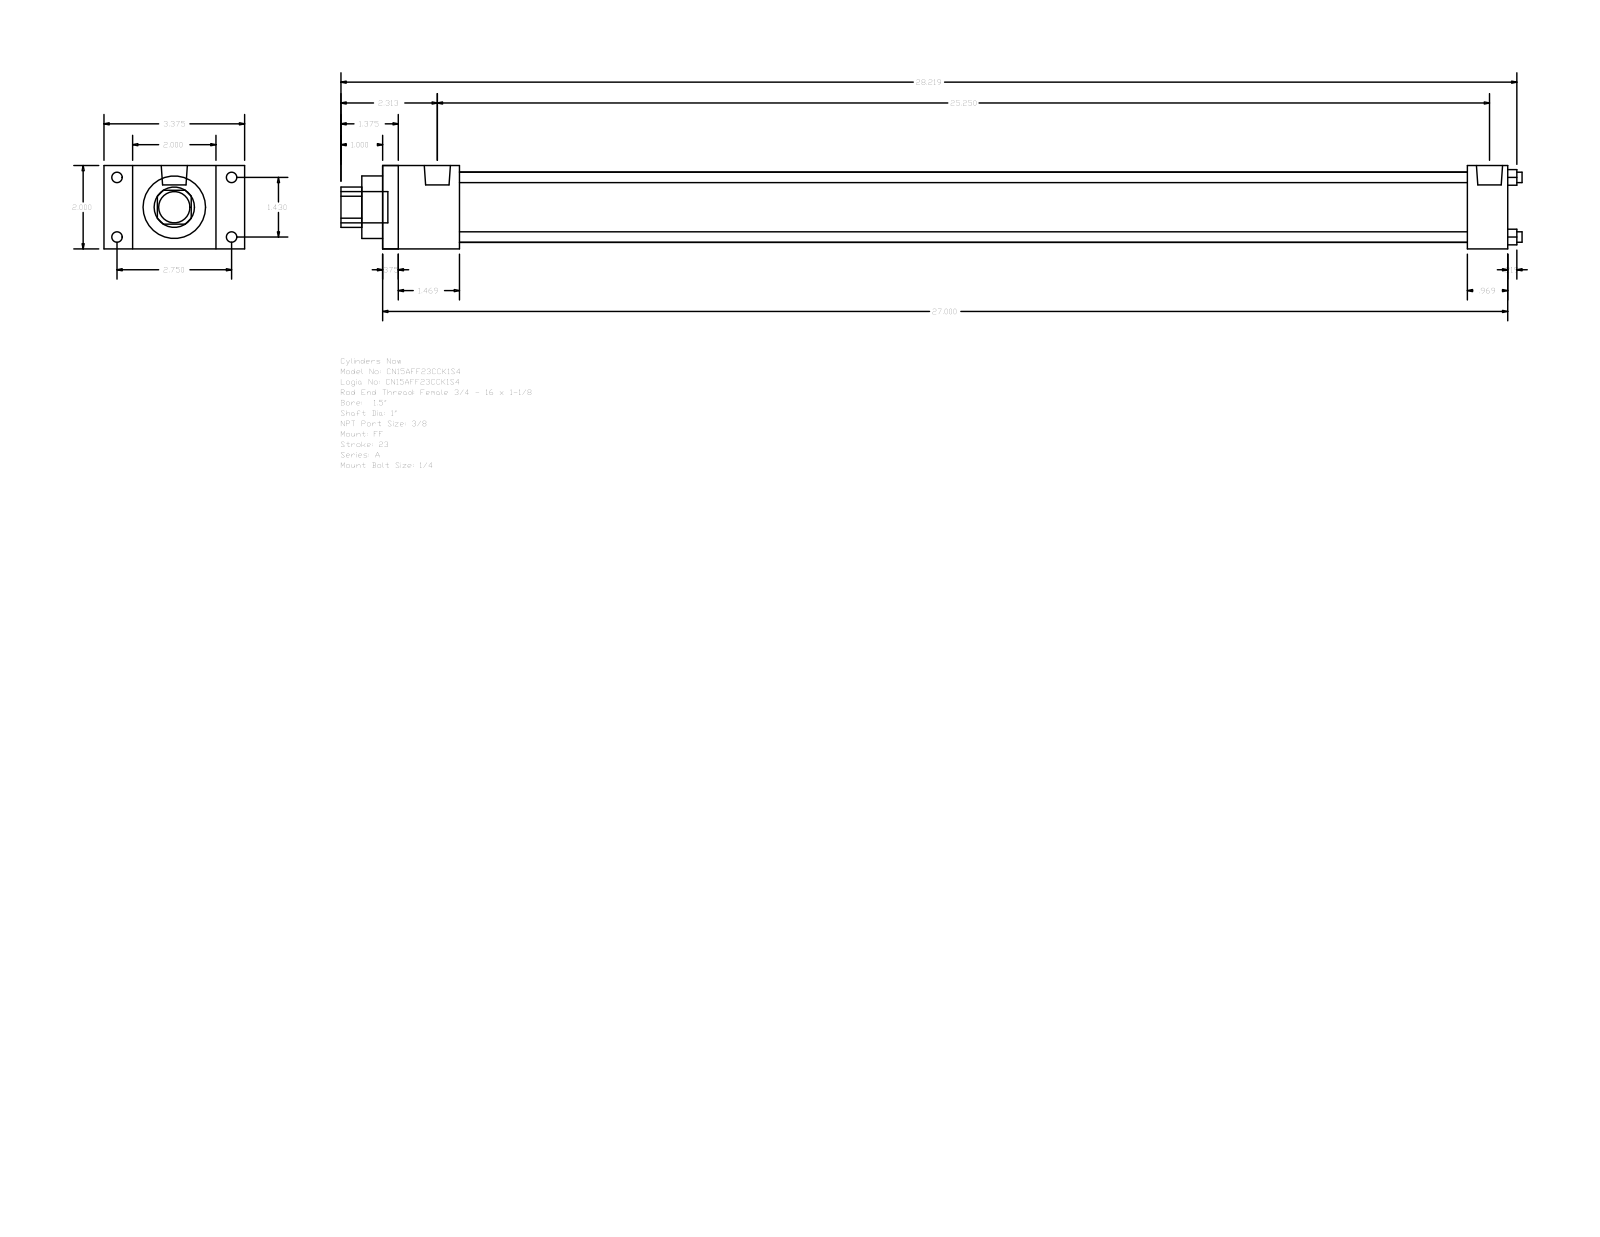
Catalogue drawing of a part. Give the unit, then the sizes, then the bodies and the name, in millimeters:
Units: millimetres
Overall size (bounding box): 719.93 × 85.72 × 50.8
Round holes (diameter × count): ⌀6.35 ×4, ⌀25.4 ×1, ⌀38.1 ×1, ⌀42.93 ×1
Round bosses / shafts (diameter × count): ⌀6.35 ×4, ⌀5.56 ×4, ⌀15.93 ×2, ⌀19.05 ×1
Partial cylindrical surfaces — rounded edges, fillets, slot ends (radius × count): R12.29 ×1
Main face-to-face distances: 50.8, 685.8, 9.52, 676.28, 46.83, 661.19, 37.31, 651.67, 614.36, 638.97
Hole centre spacings: 25.68, 36.32, 51.36
Bodies: 0 solids, 92 faces (64 planar, 28 cylindrical, 0 other)
Part name (STEP PRODUCT): A_FF__0150_1
STEP written by: GSSL Pune (CONFIG_CONTROL_DESIGN)
